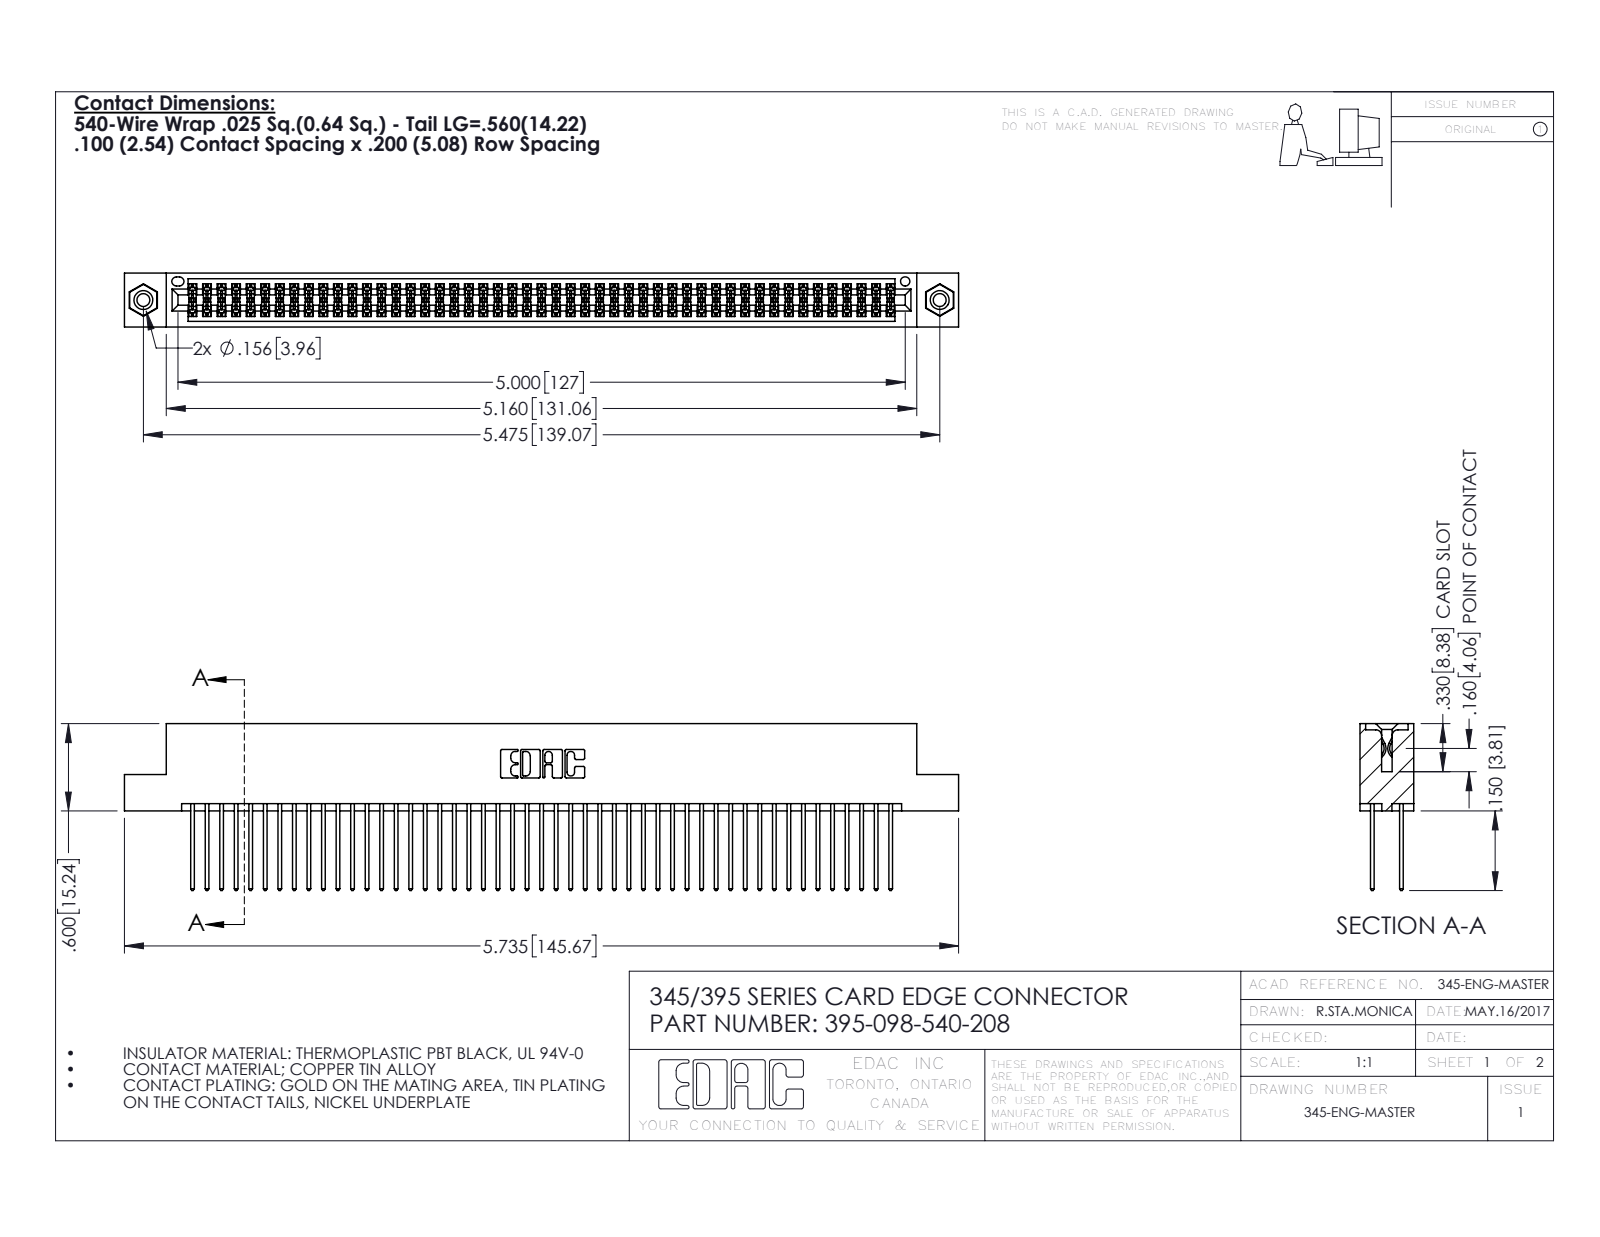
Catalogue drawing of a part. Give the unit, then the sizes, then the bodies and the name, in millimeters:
Units: millimetres
Overall size (bounding box): 145.7 × 29.1 × 9.4
Round holes (diameter × count): ⌀2.3 ×2, ⌀3.2 ×2, ⌀4 ×2, ⌀1.6 ×1
Round bosses / shafts (diameter × count): ⌀3.9 ×2
Partial cylindrical surfaces — rounded edges, fillets, slot ends (radius × count): R0.2 ×147, R0.3 ×98, R0.3 ×22, R0.2 ×6, R0.8 ×6, R0.7 ×3, R0.4 ×2, R0.5 ×2
Main face-to-face distances: 1.8, 7.6, 5.1, 2.5, 6.9, 0.6, 9.4, 5.7, 4.4, 3.8
Hole centre spacings: 6.9, 133.1, 139.1
Volume: 14 600 mm³ · Surface area: 23 430 mm²
Bodies: 101 solids, 5086 faces (3346 planar, 1724 cylindrical, 16 other)
Part name (STEP PRODUCT): 345 Part_Flush Mounting Lugs - 0.156 Dia-TI; 345-250-001_345-250-003-102; 345-292-001_345-293-140; 395-098-540-208
STEP written by: SolidWorks 2016 (CONFIG_CONTROL_DESIGN)
